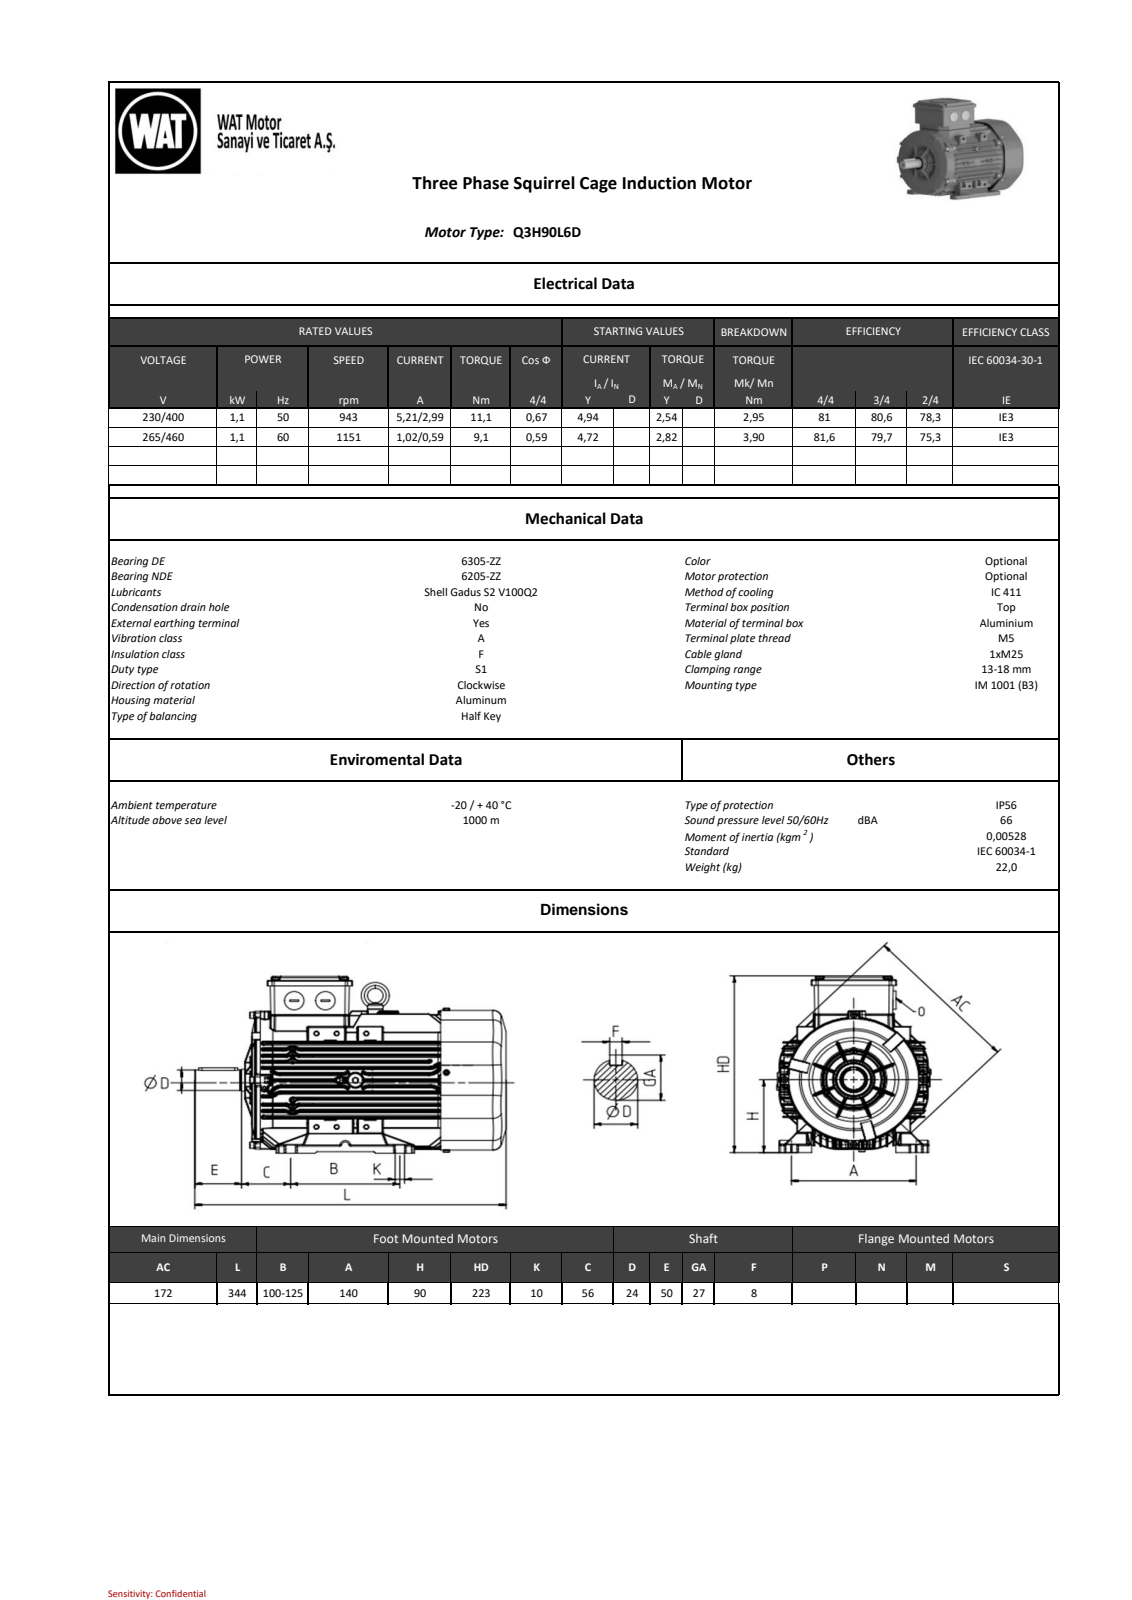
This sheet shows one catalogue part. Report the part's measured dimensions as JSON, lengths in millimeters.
{"part_name": "model1", "step_written_by": "SIEMENS PLM Software NX2206.8101 (AUTOMOTIVE_DESIGN)", "units": "millimeters", "bodies": {"solids": 0, "faces": 6614, "planar": 1526, "cylindrical": 2800, "other": 2288}, "overall_size": [343.54, 223.05, 178.35], "round_holes": [[6.8, 1], [8.4, 1], [9.87, 1], [37.42, 1], [79.79, 1], [97.79, 1], [115.78, 1]], "round_bosses_or_shafts": [[5, 12], [8, 7], [10, 5], [9.5, 4], [25, 3], [102.19, 1], [84.19, 1], [39.5, 1]], "partial_cylinders_radius": [[1, 899], [0.8, 537], [0.98, 104], [2, 86], [0.5, 76], [8, 28], [1.5, 26], [3, 16]], "face_to_face_distances": [7.5, 91.91, 8.93, 82.98, 23.57, 50.35, 7.37, 90.35, 16.87, 75.04]}
